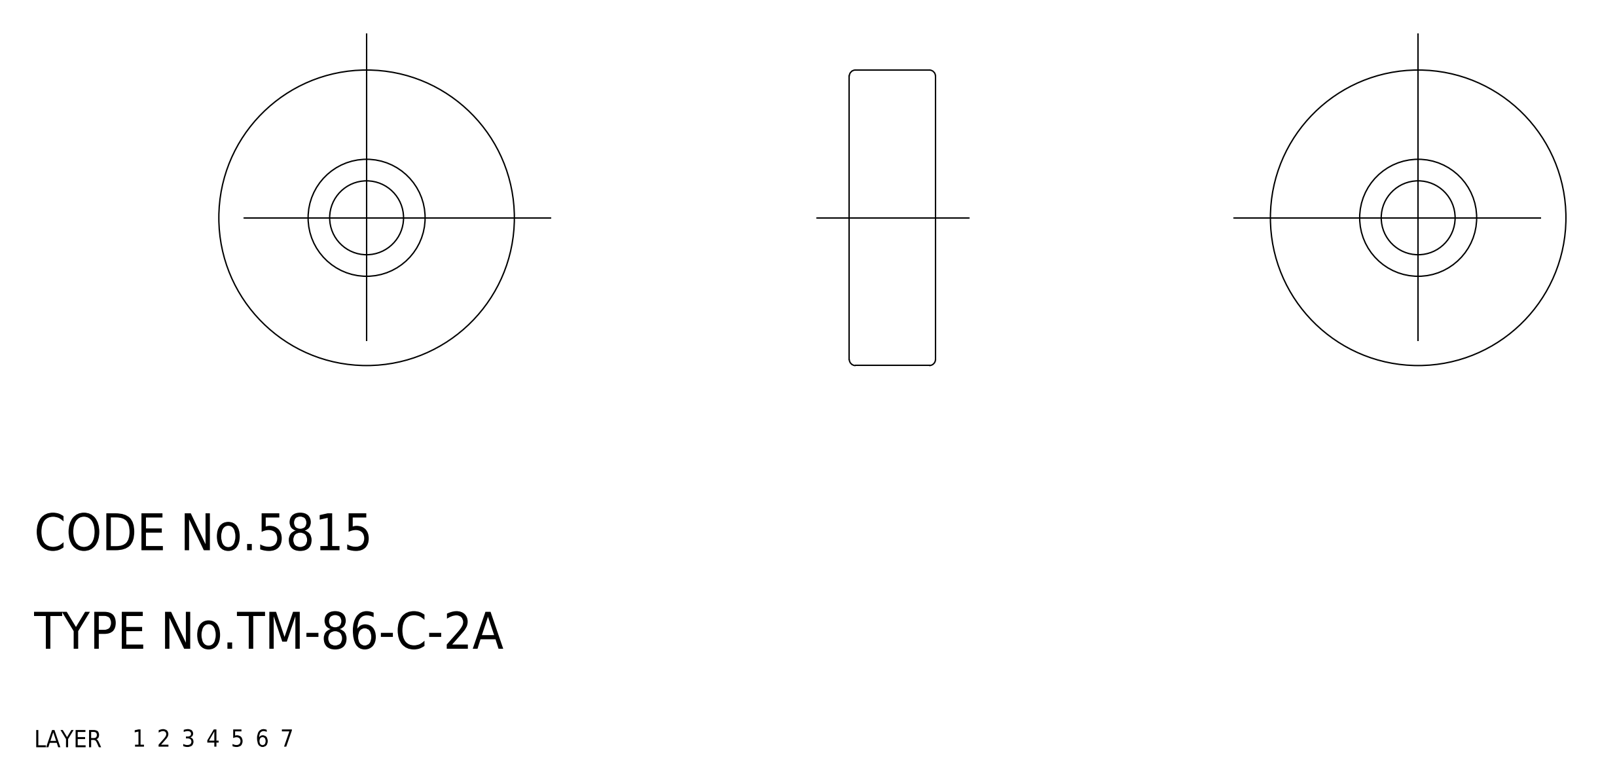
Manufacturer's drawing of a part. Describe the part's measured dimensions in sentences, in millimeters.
The part is named "roller". Its 3-D file was written by "CADfix (AUTOMOTIVE_DESIGN)". It is 1 solid with 28 faces: 0 planar, 0 cylindrical and 28 other. Overall it measures 24 by 24 by 7 millimeters. Its volume is 2 967 cubic millimeters and its surface area 1 977 square millimeters.
